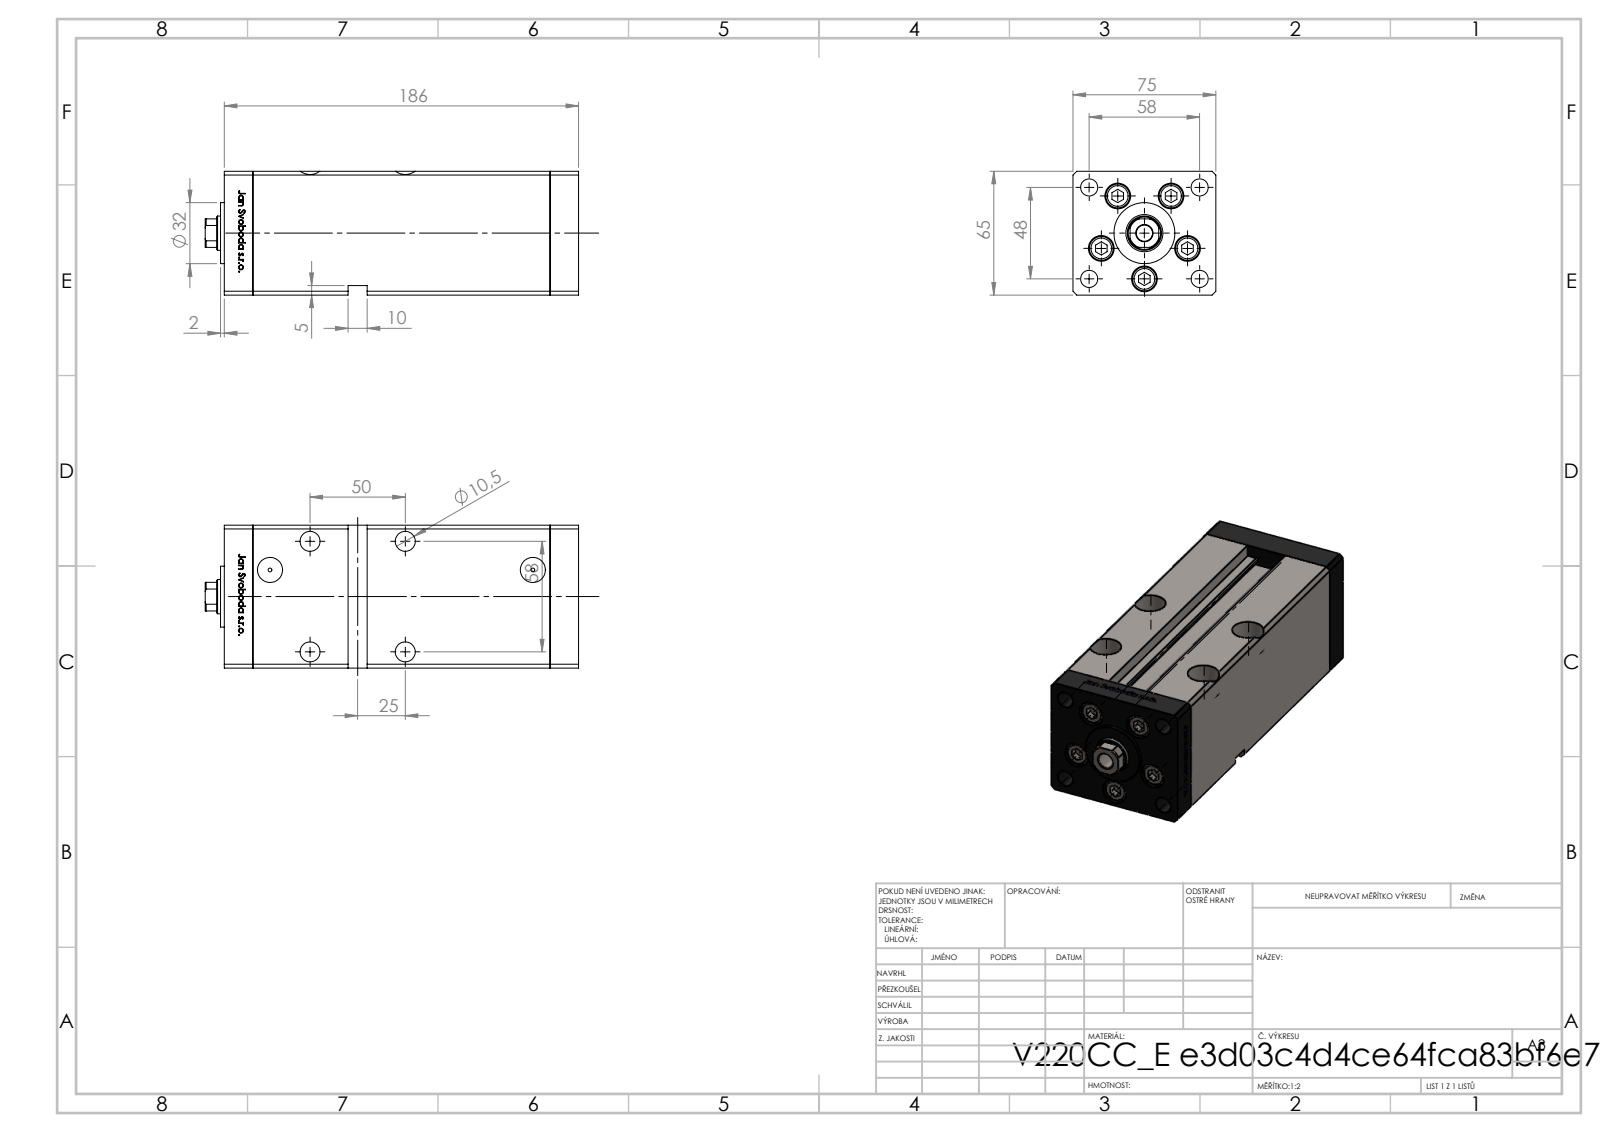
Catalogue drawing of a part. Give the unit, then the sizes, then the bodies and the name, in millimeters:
Units: millimetres
Overall size (bounding box): 196 × 75 × 65
Round holes (diameter × count): ⌀9 ×9, ⌀13.5 ×5, ⌀10.5 ×4, ⌀16.5 ×4, ⌀2 ×2, ⌀13.16 ×2, ⌀8.5 ×1, ⌀18 ×1, ⌀19.5 ×1
Round bosses / shafts (diameter × count): ⌀12.5 ×5, ⌀8 ×5, ⌀32 ×1
Partial cylindrical surfaces — rounded edges, fillets, slot ends (radius × count): R0.93 ×2, R8.5 ×1
Main face-to-face distances: 75, 65, 15, 156, 171, 186, 28, 54.5, 10.5, 26.25
Hole centre spacings: 24, 37.64, 58, 15.67, 17.22, 27.71, 28.83, 29
Volume: 769 603 mm³ · Surface area: 146 638 mm²
Bodies: 14 solids, 1212 faces (473 planar, 165 cylindrical, 574 other)
Part name (STEP PRODUCT): V220C BACK_E; V220C_VC_E; V220C_E MIDDLE; V220C_FRONT_E (+1 more)
STEP written by: SolidWorks 2019 (CONFIG_CONTROL_DESIGN)
